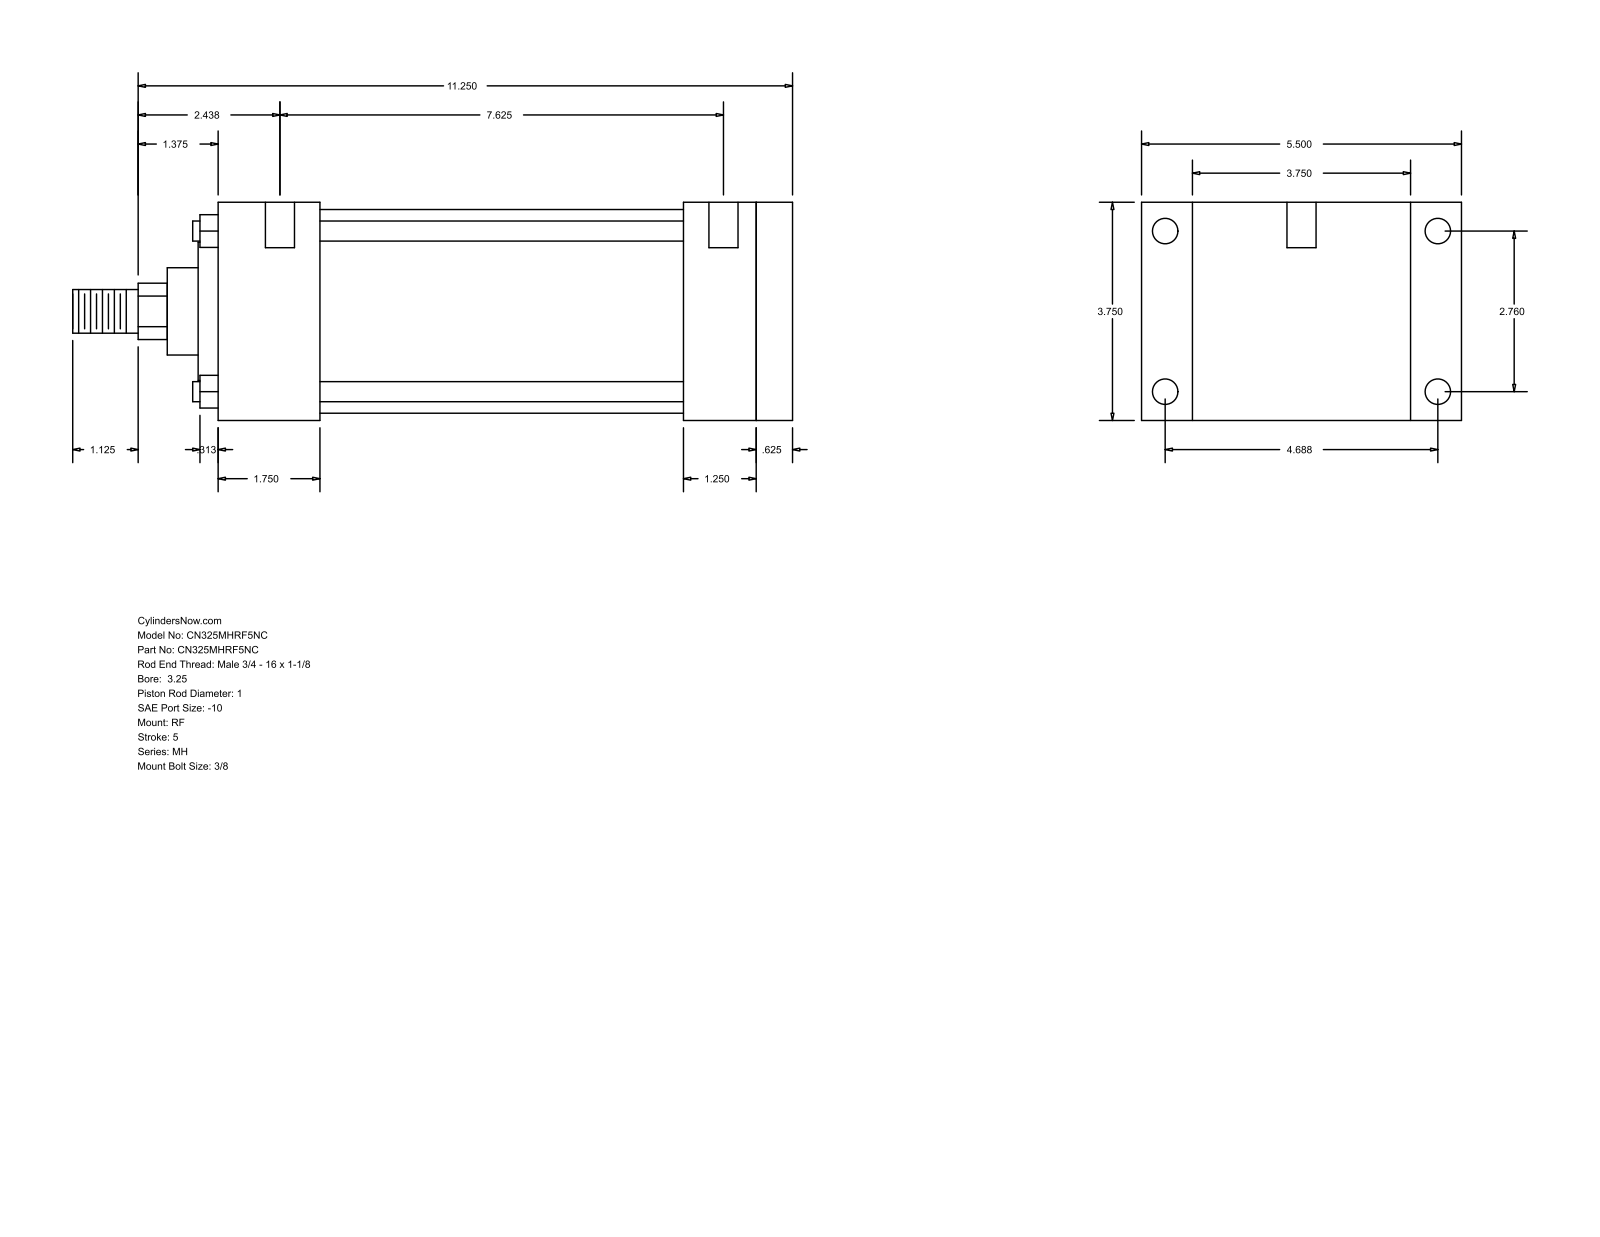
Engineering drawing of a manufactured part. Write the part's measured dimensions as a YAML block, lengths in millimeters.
part_name: "MH_RF__0325_1"
step_written_by: "GSSL Pune (CONFIG_CONTROL_DESIGN)"
units: millimeters
bodies: {solids: 0, faces: 94, planar: 65, cylindrical: 29, other: 0}
overall_size: [314.32, 139.7, 95.25]
round_holes:
  - {diameter: 5.56, count: 4}
  - {diameter: 11.13, count: 4}
  - {diameter: 12.7, count: 2}
round_bosses_or_shafts:
  - {diameter: 8.76, count: 4}
  - {diameter: 88.9, count: 1}
  - {diameter: 60.33, count: 1}
  - {diameter: 38.1, count: 1}
  - {diameter: 25.4, count: 1}
  - {diameter: 19.05, count: 1}
partial_cylinders:
  - {radius: 12.29, count: 1}
face_to_face_distances: [95.24, 250.83, 234.96, 15.87, 22.23, 117.47, 44.46, 190.5, 206.37, 203.2]
hole_center_spacings: [70.1, 119.06, 138.16, 200.02, 1.58, 4.76, 193.68, 195.26]
